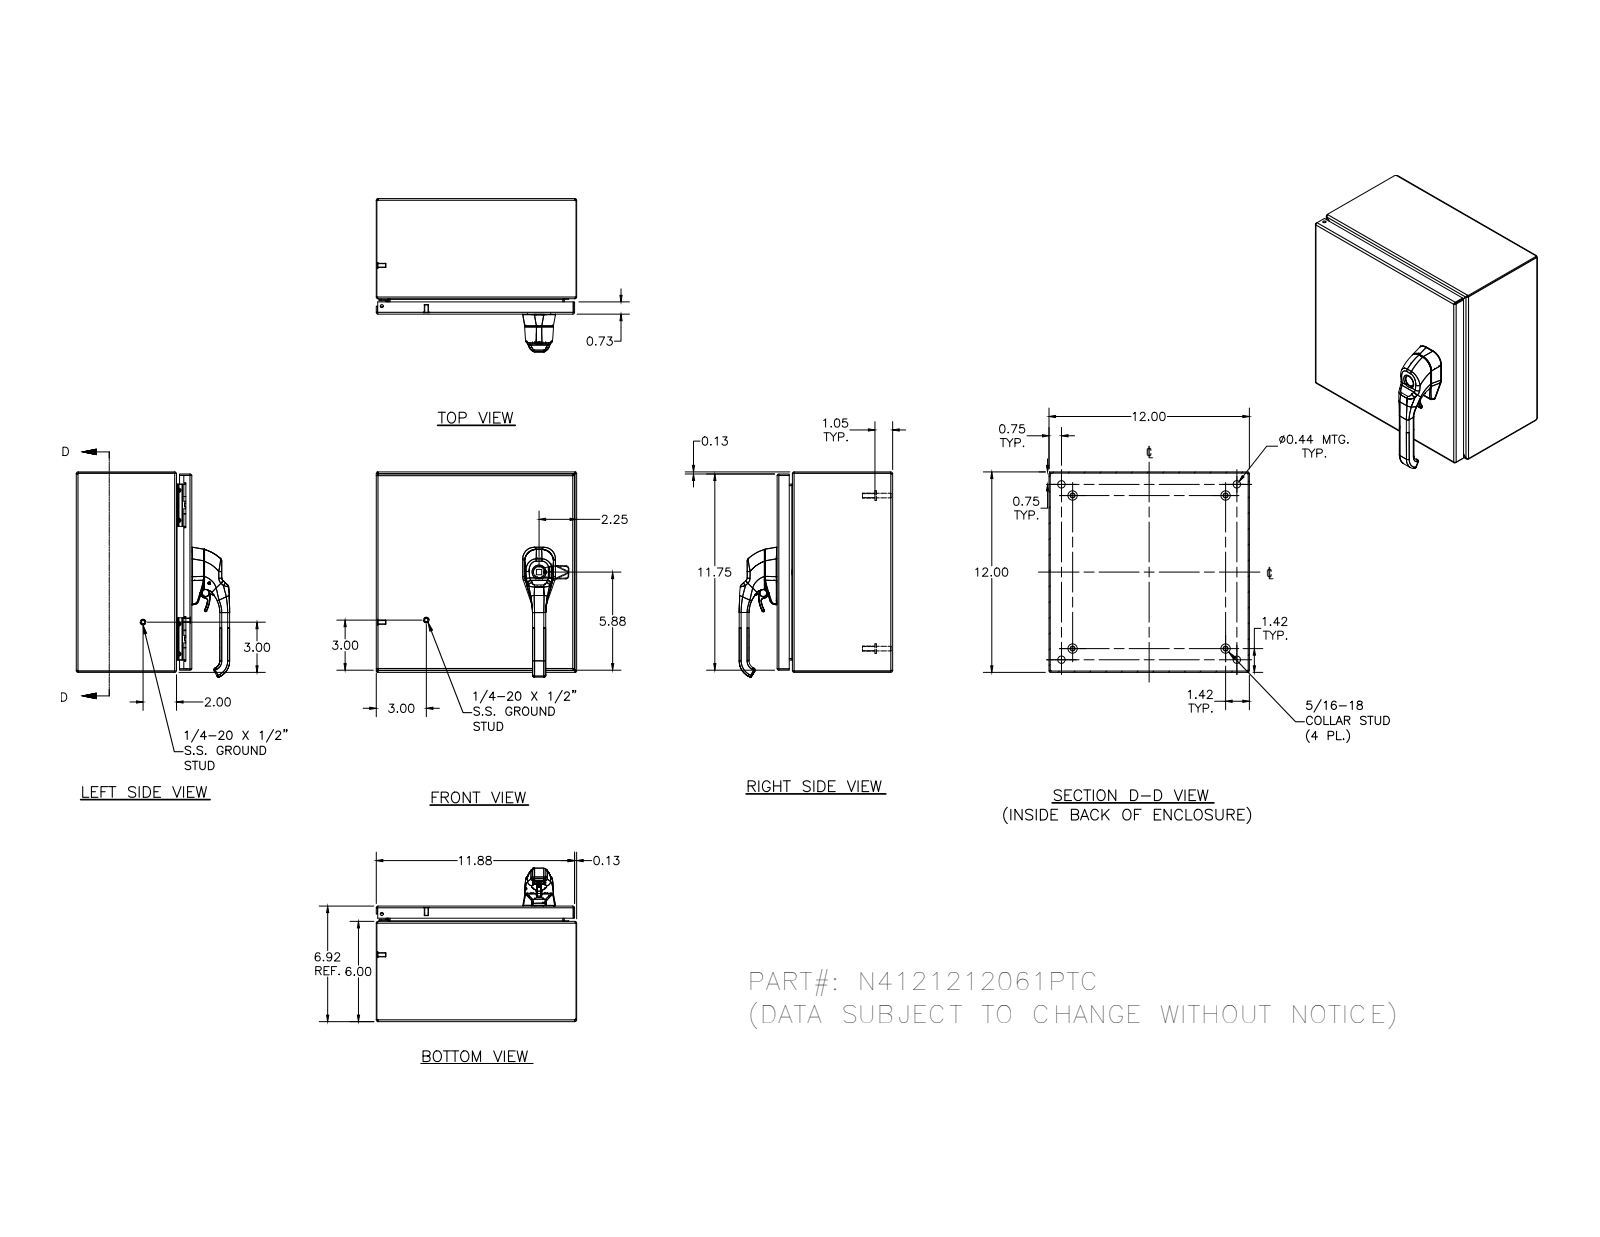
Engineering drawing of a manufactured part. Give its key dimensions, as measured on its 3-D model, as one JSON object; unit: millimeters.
{"part_name": "N4121212061PTC", "step_written_by": "SolidWorks 2018 (AUTOMOTIVE_DESIGN)", "units": "millimeters", "bodies": {"solids": 28, "faces": 1280, "planar": 417, "cylindrical": 474, "other": 389}, "overall_size": [304.8, 304.8, 231], "volume_mm3": 982600, "surface_area_mm2": 909700, "round_holes": [[4.8, 5], [2.4, 4], [3.9, 4], [4.2, 4], [4.4, 4], [11.1, 4], [7.1, 3], [4, 2], [4.7, 1]], "round_bosses_or_shafts": [[6.4, 10], [14.3, 4], [9.1, 4], [8.1, 4], [7.6, 4], [7, 4], [6.5, 4], [4.2, 4]], "partial_cylinders_radius": [[0.8, 30], [1.3, 26], [2.7, 20], [0.4, 18], [3.2, 14], [0.8, 8], [1.7, 8], [1.7, 8]], "face_to_face_distances": [1.9, 302.9, 173.8, 175.7, 304.8, 301, 171.9, 150.5, 23.3, 18.8], "hole_center_spacings": [203.1, 266.7, 0.4, 16.8, 219.9, 0.5, 12.7, 16.5]}
